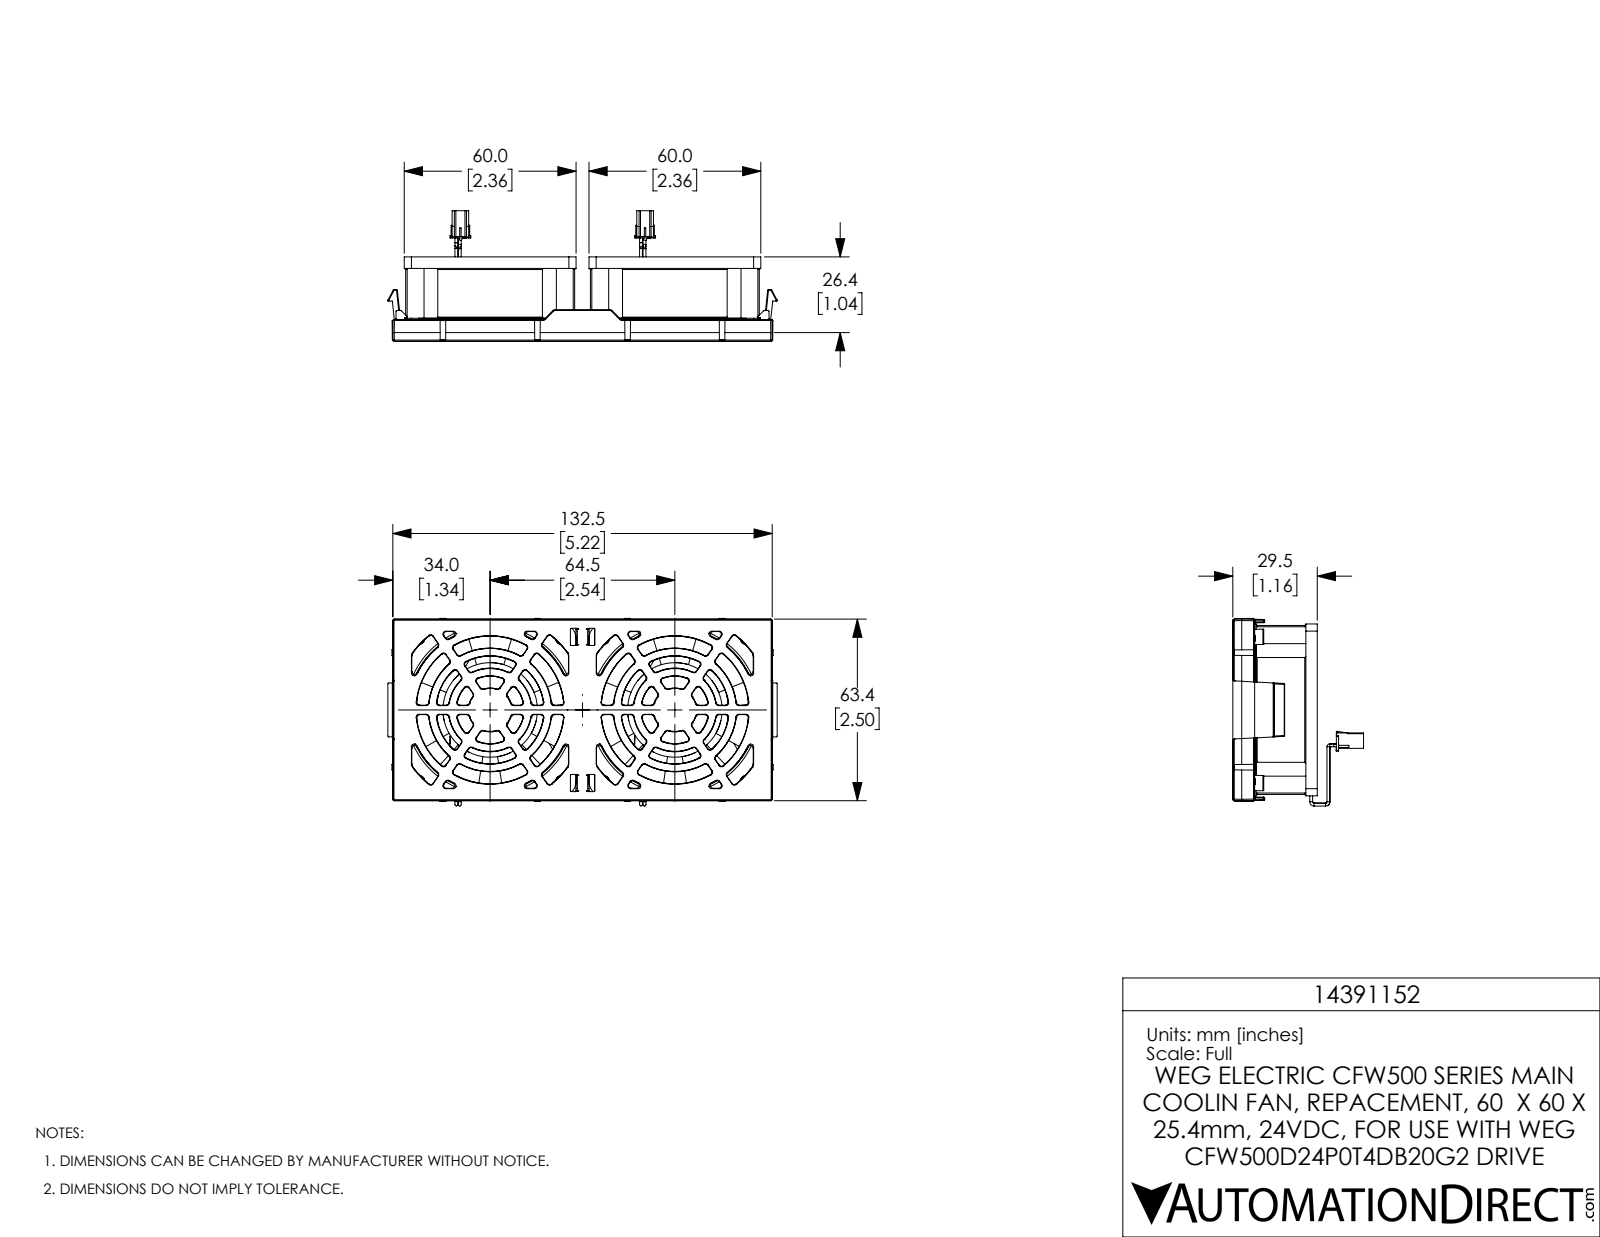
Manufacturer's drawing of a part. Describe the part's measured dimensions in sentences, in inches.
The part is named "10003693872swa000 w ext Grill COMPLETE 1". Its 3-D file was written by "SolidWorks 2017 (AUTOMOTIVE_DESIGN)". It is 11 solids with 3519 faces: 1192 planar, 659 cylindrical and 1668 other. Overall it measures 5.352 by 2.579 by 1.797 inches. Its volume is 6.092 cubic inches and its surface area 128 square inches. Round holes: 8 of diameter 0.169, 2 of diameter 2.264. Round bosses or shafts: 20 of diameter 0.039, 2 of diameter 2.323, 2 of diameter 1.299. Partial cylindrical surfaces (rounded edges, fillets, slot ends): 133 of radius 0.012, 36 of radius 0.02, 16 of radius 0.004, 14 of radius 0.65, 14 of radius 1.122, 12 of radius 0.039, 10 of radius 0.197, 8 of radius 0.01. The main face-to-face distances are 0.157, 0.137, 0.843, 1.024, 1.161, 0.02, 0.161, 1, 0.024, 0.079. The hole center spacings are 1.392, 1.969, 2.539, 1.841, 2.784, 3.213, 3.659, 0.571.
